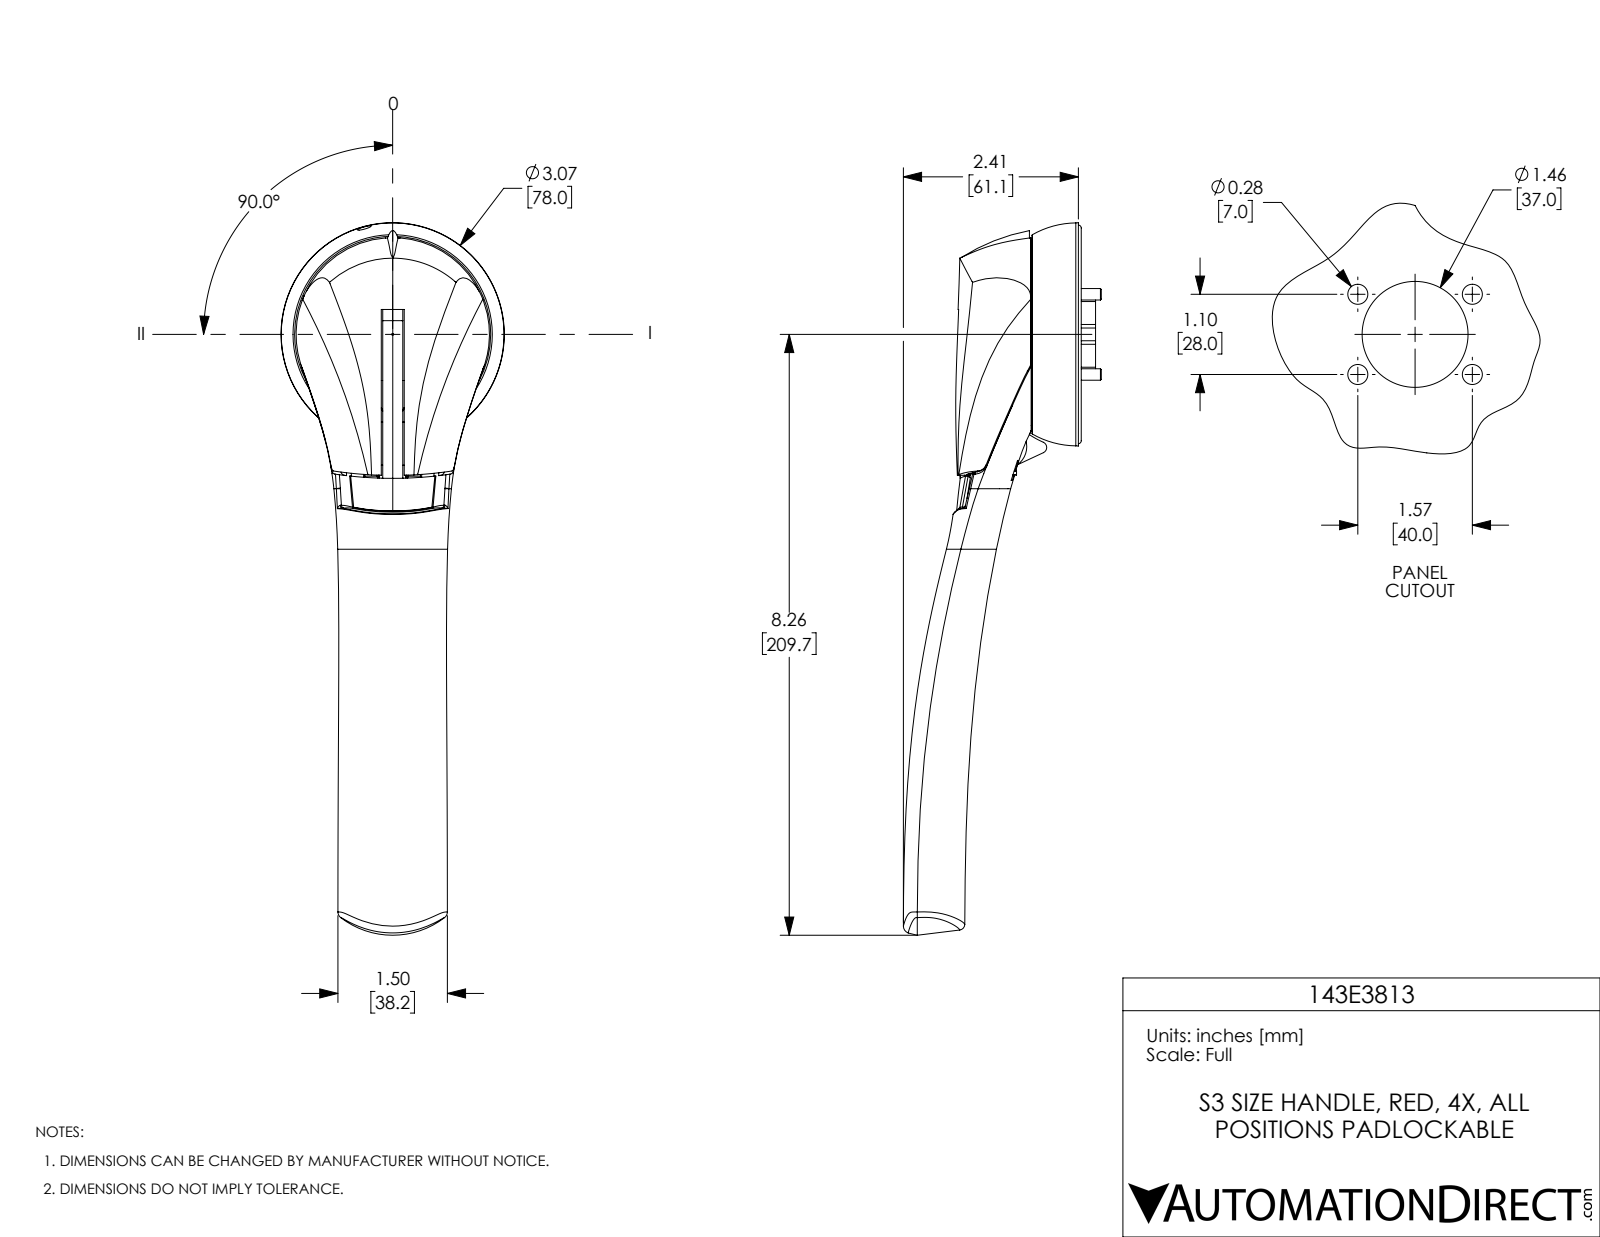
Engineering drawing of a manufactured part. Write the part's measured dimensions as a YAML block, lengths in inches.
part_name: "143E3813"
step_written_by: "SolidWorks 2017 (AUTOMOTIVE_DESIGN)"
units: inches
bodies: {solids: 8, faces: 1514, planar: 806, cylindrical: 544, other: 164}
overall_size: [9.793, 3.07, 2.721]
volume: 12.91
surface_area: 100.4
round_holes:
  - {diameter: 0.157, count: 6}
  - {diameter: 0.339, count: 4}
  - {diameter: 0.425, count: 4}
  - {diameter: 0.03, count: 3}
  - {diameter: 0.169, count: 2}
  - {diameter: 0.362, count: 2}
  - {diameter: 0.118, count: 1}
  - {diameter: 0.189, count: 1}
  - {diameter: 2.992, count: 1}
round_bosses_or_shafts:
  - {diameter: 0.02, count: 11}
  - {diameter: 0.335, count: 4}
  - {diameter: 0.315, count: 4}
  - {diameter: 0.089, count: 3}
  - {diameter: 0.069, count: 3}
  - {diameter: 0.228, count: 2}
  - {diameter: 2.819, count: 1}
  - {diameter: 2.701, count: 1}
partial_cylinders:
  - {radius: 0.01, count: 221}
  - {radius: 0.015, count: 20}
  - {radius: 0.034, count: 20}
  - {radius: 0.03, count: 15}
  - {radius: 0.039, count: 4}
  - {radius: 0.025, count: 3}
  - {radius: 5.437, count: 3}
  - {radius: 0.079, count: 2}
face_to_face_distances: [0.024, 0.701, 0.713, 0.689, 0.035, 0.276, 0.102, 0.173, 0.244, 0.047]
hole_center_spacings: [0.961, 0.309, 0.669, 1.098, 1.102, 1.203, 1.575, 1.881]
